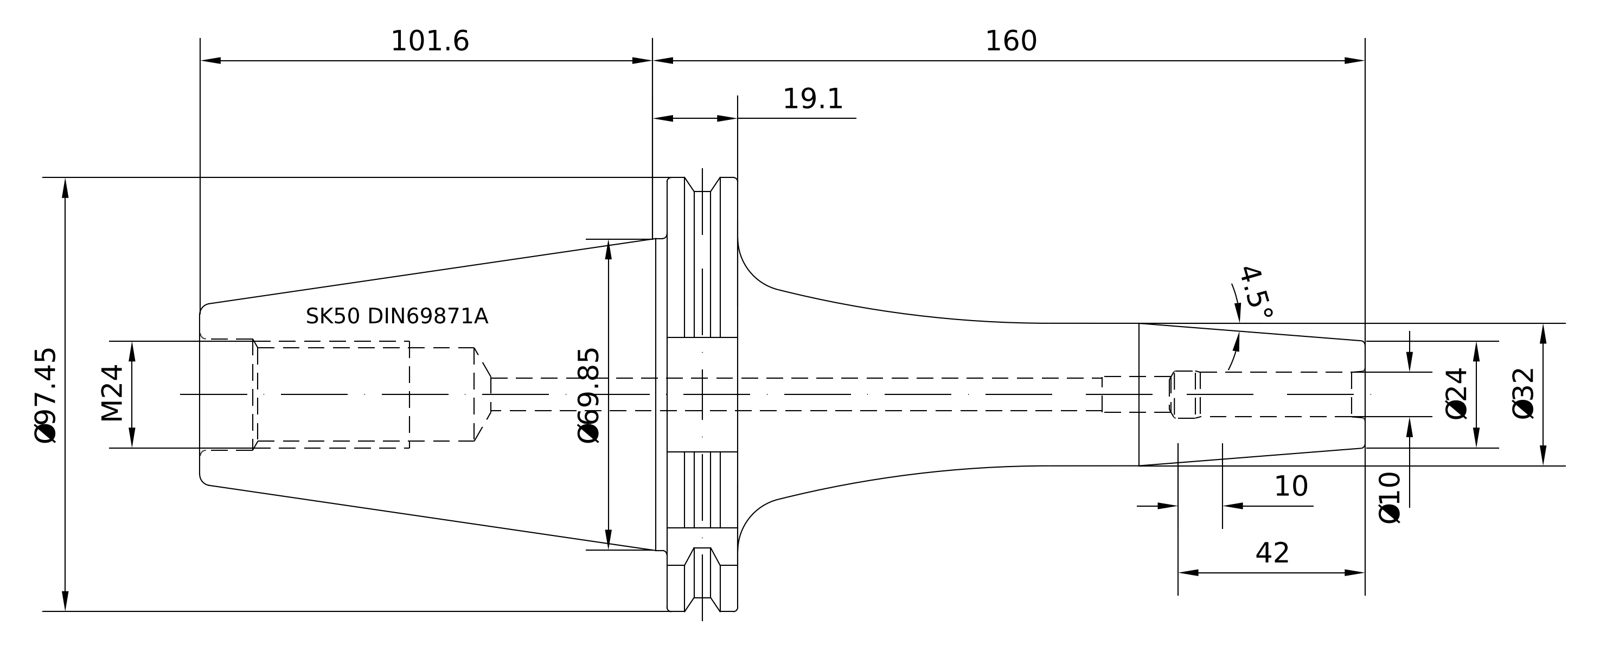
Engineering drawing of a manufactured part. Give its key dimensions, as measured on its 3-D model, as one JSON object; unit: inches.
{"part_name": "50-442-10", "step_written_by": "PRO/ENGINEER BY PARAMETRIC TECHNOLOGY CORPORATION, 2010430 (CONFIG_CONTROL_DESIGN)", "units": "inches", "bodies": {"solids": 1, "faces": 95, "planar": 21, "cylindrical": 24, "other": 50}, "overall_size": [10.299, 3.837, 3.701], "volume_in3": 28.71, "surface_area_in2": 88.35, "round_holes": [[0.394, 1], [0.817, 1], [0.985, 1], [1.012, 1]], "round_bosses_or_shafts": [[3.583, 1], [2.722, 1], [1.26, 1], [0.945, 1]], "partial_cylinders_radius": [[0.069, 1], [1.919, 1]], "face_to_face_distances": [0.624, 2.866, 4.126, 4.75, 10.299, 6.173, 5.549, 1.016, 1.89, 2.236]}
